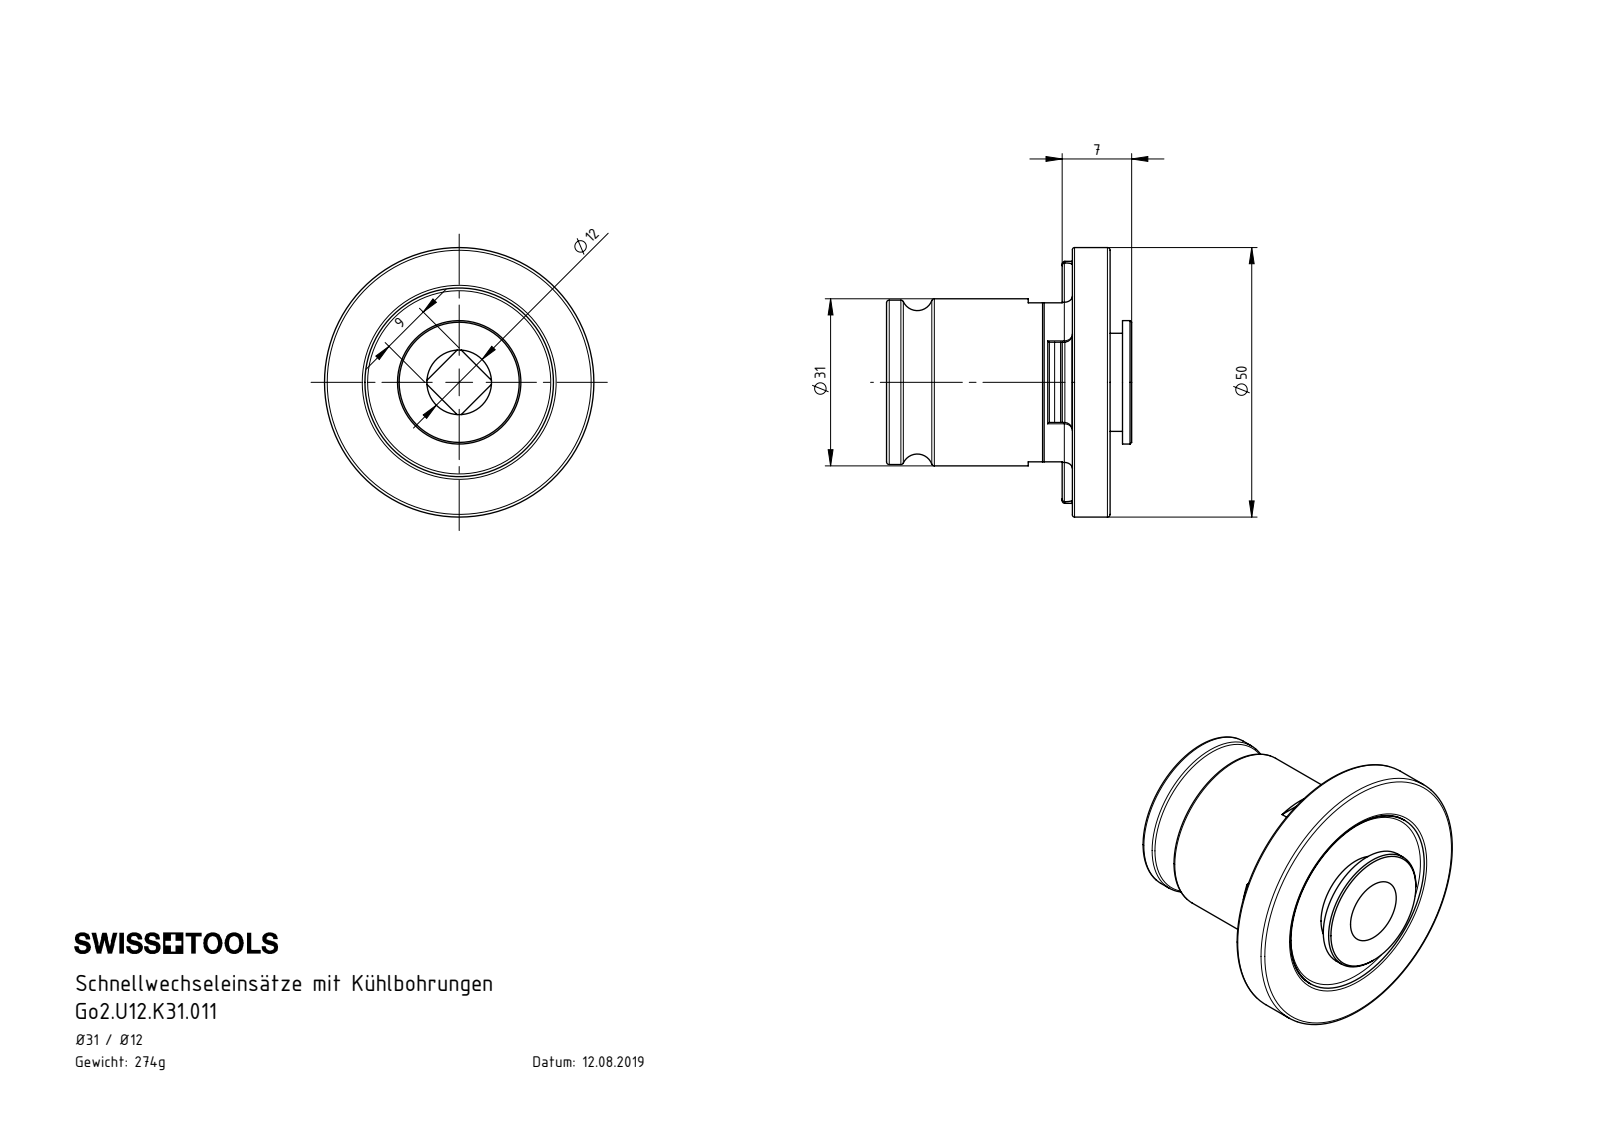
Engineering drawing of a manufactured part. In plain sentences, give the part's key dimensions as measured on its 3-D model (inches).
The part is named "Go2.U12.K31.011". Its 3-D file was written by "SolidWorks 2017 (AUTOMOTIVE_DESIGN)". It is 1 solid with 102 faces: 37 planar, 28 cylindrical and 37 other. Overall it measures 1.969 by 1.969 by 1.791 inches. Its volume is 2.133 cubic inches and its surface area 16.65 square inches. Round holes: 1 of diameter 0.472, 1 of diameter 0.791. Round bosses or shafts: 1 of diameter 1.969, 1 of diameter 1.378, 1 of diameter 1.22, 1 of diameter 1.205, 1 of diameter 1.201, 1 of diameter 0.902, 1 of diameter 0.717. Partial cylindrical surfaces (rounded edges, fillets, slot ends): 5 of radius 0.059, 4 of radius 0.02, 1 of radius 0.787, 1 of radius 0.884. The main face-to-face distances are 0.276, 0.25, 0.026, 1.358, 1.608, 1.634, 1.791, 0.433, 0.183, 0.157.
